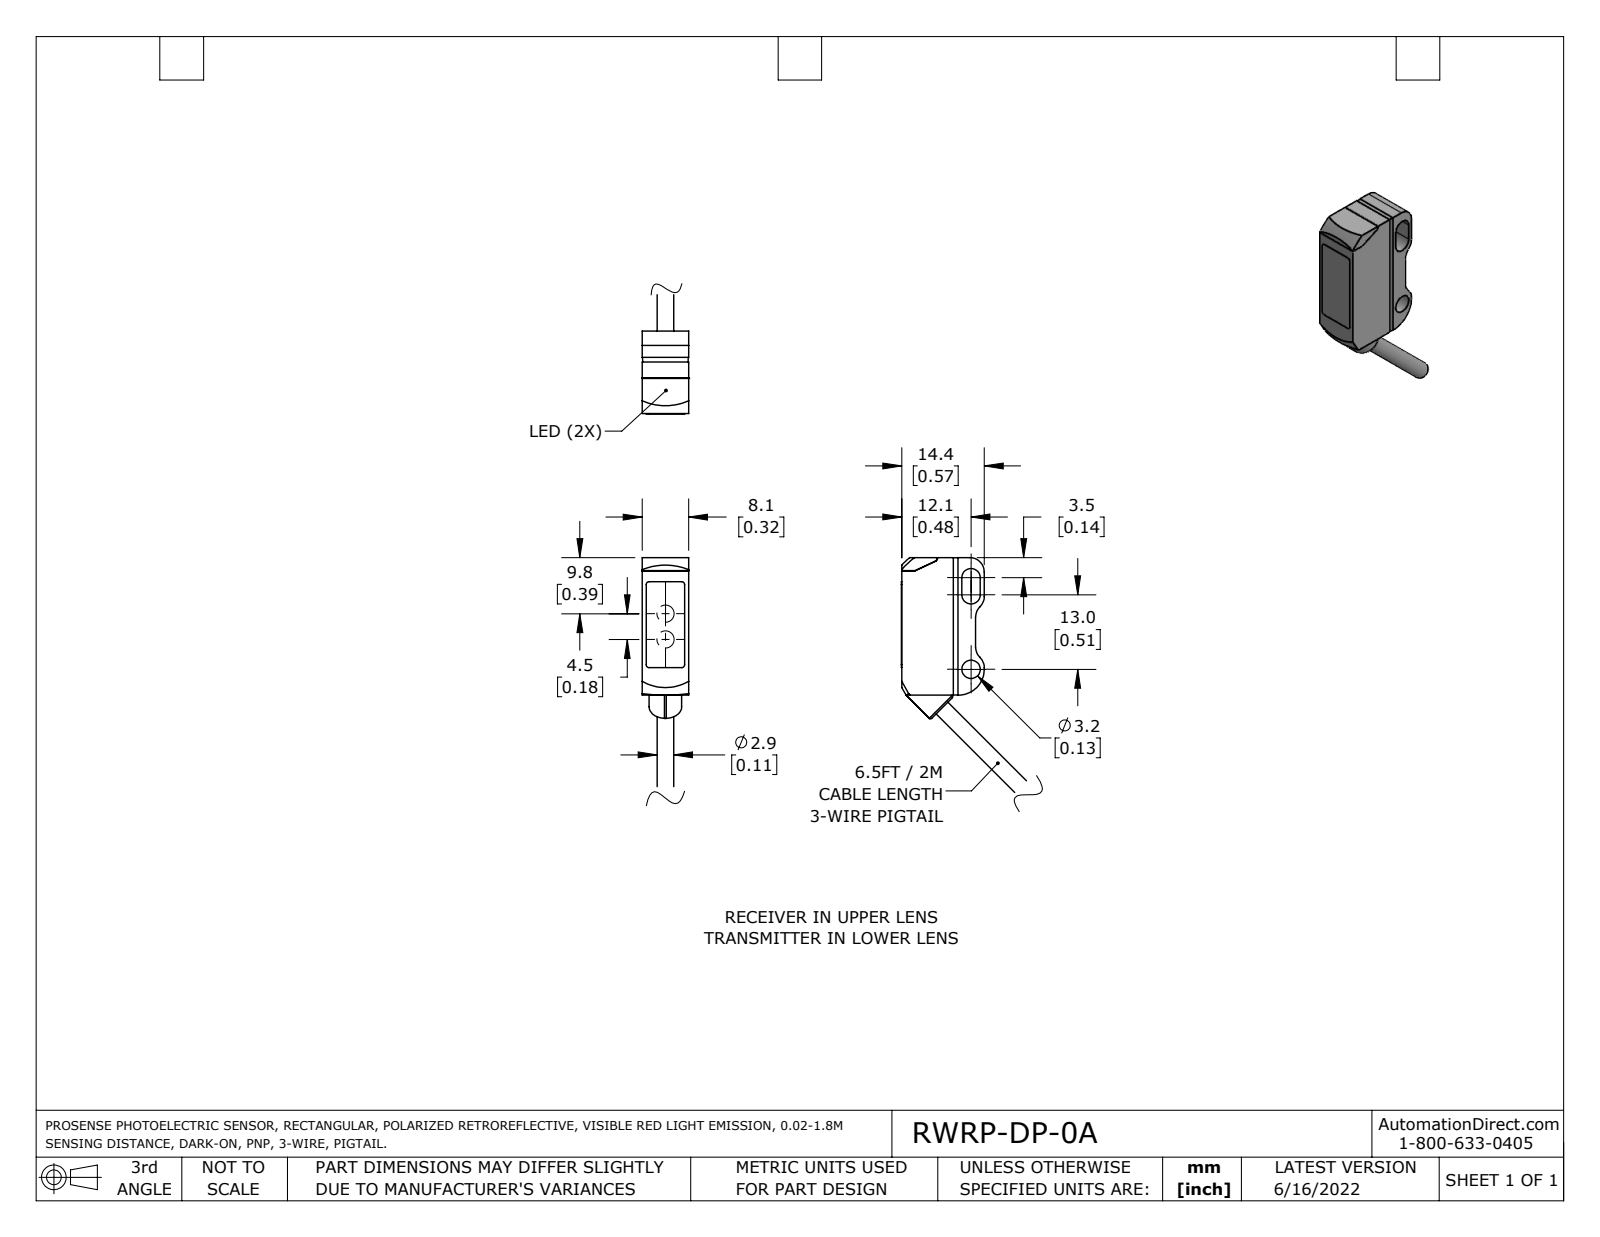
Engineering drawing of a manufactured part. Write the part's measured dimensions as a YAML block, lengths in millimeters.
part_name: "O8H200"
step_written_by: "PARTsolutions (CONFIG_CONTROL_DESIGN)"
units: millimeters
bodies: {solids: 1, faces: 66, planar: 42, cylindrical: 19, other: 5}
overall_size: [41.01, 21.83, 8.1]
volume: 2630
surface_area: 1659
round_holes:
  - {diameter: 3.2, count: 1}
  - {diameter: 4.42, count: 1}
round_bosses_or_shafts:
  - {diameter: 5.69, count: 1}
  - {diameter: 2.9, count: 1}
partial_cylinders:
  - {radius: 2.5, count: 5}
  - {radius: 0.5, count: 4}
  - {radius: 0.6, count: 2}
  - {radius: 1.6, count: 2}
  - {radius: 4.5, count: 1}
  - {radius: 15.7, count: 1}
face_to_face_distances: [8.1, 12.9, 12.97, 1.5, 14.4, 14.47, 3.9, 24, 0.7, 0.8]
